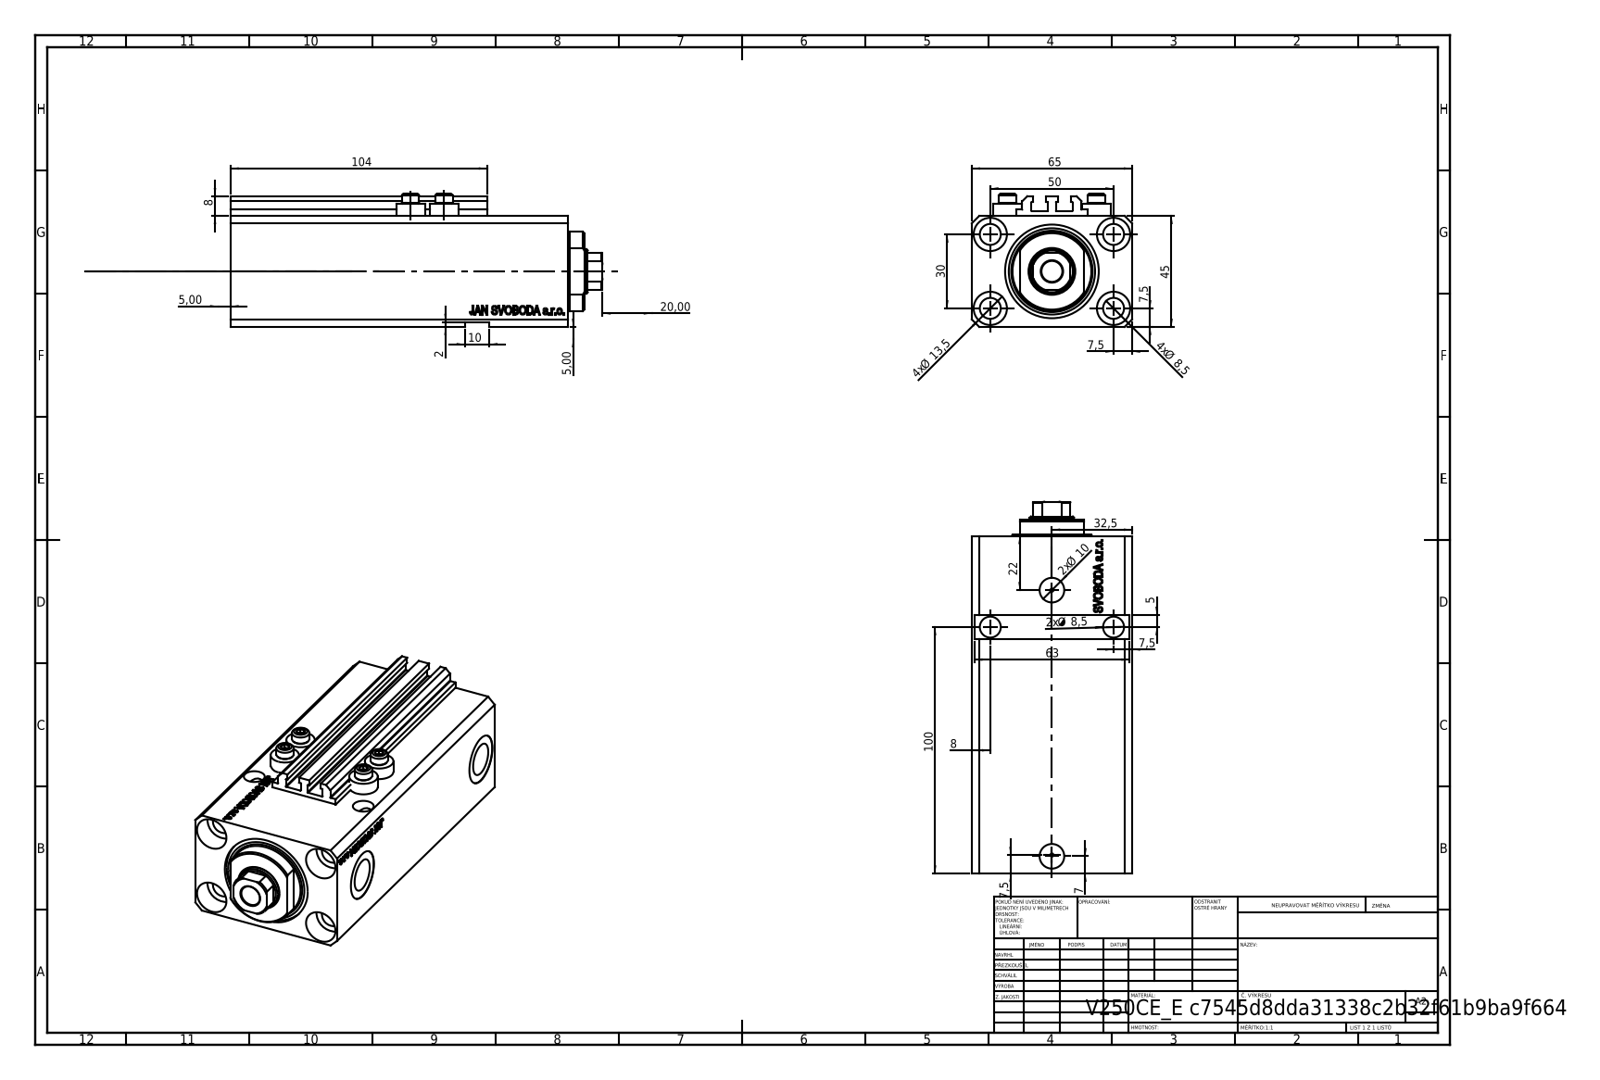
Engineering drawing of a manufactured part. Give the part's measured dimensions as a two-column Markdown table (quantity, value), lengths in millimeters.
| quantity | value |
| --- | --- |
| part name | V250CE_VC_E; V250CE_C_VCP; V250CE_E_Body; ALLEN BOLT V250CE |
| STEP written by | SolidWorks 2019 (CONFIG_CONTROL_DESIGN) |
| units | millimeters |
| bodies | 8 solids, 1067 faces (511 planar, 126 cylindrical, 430 other) |
| overall size | 150.9 × 65 × 54 |
| volume | 353 953 mm³ |
| surface area | 94 631 mm² |
| round holes (diameter × count) | 8.5 × 7, 1.25 × 4, 4 × 4, 13.5 × 4, 10 × 2, 13.16 × 2, 20 × 2, 18 × 1, 25 × 1, 38 × 1 |
| round bosses / shafts (diameter × count) | 11.6 × 4, 7 × 4 |
| partial cylindrical surfaces (radius × count) | 0.2 × 10, 8.5 × 1, 16 × 1 |
| main face-to-face distances | 45, 65, 2, 47, 111.9, 2.5, 10, 137, 25.1, 6.9 |
| hole center spacings | 29.15, 50, 13.6, 15.12, 27.89, 30, 33.62, 36 |
